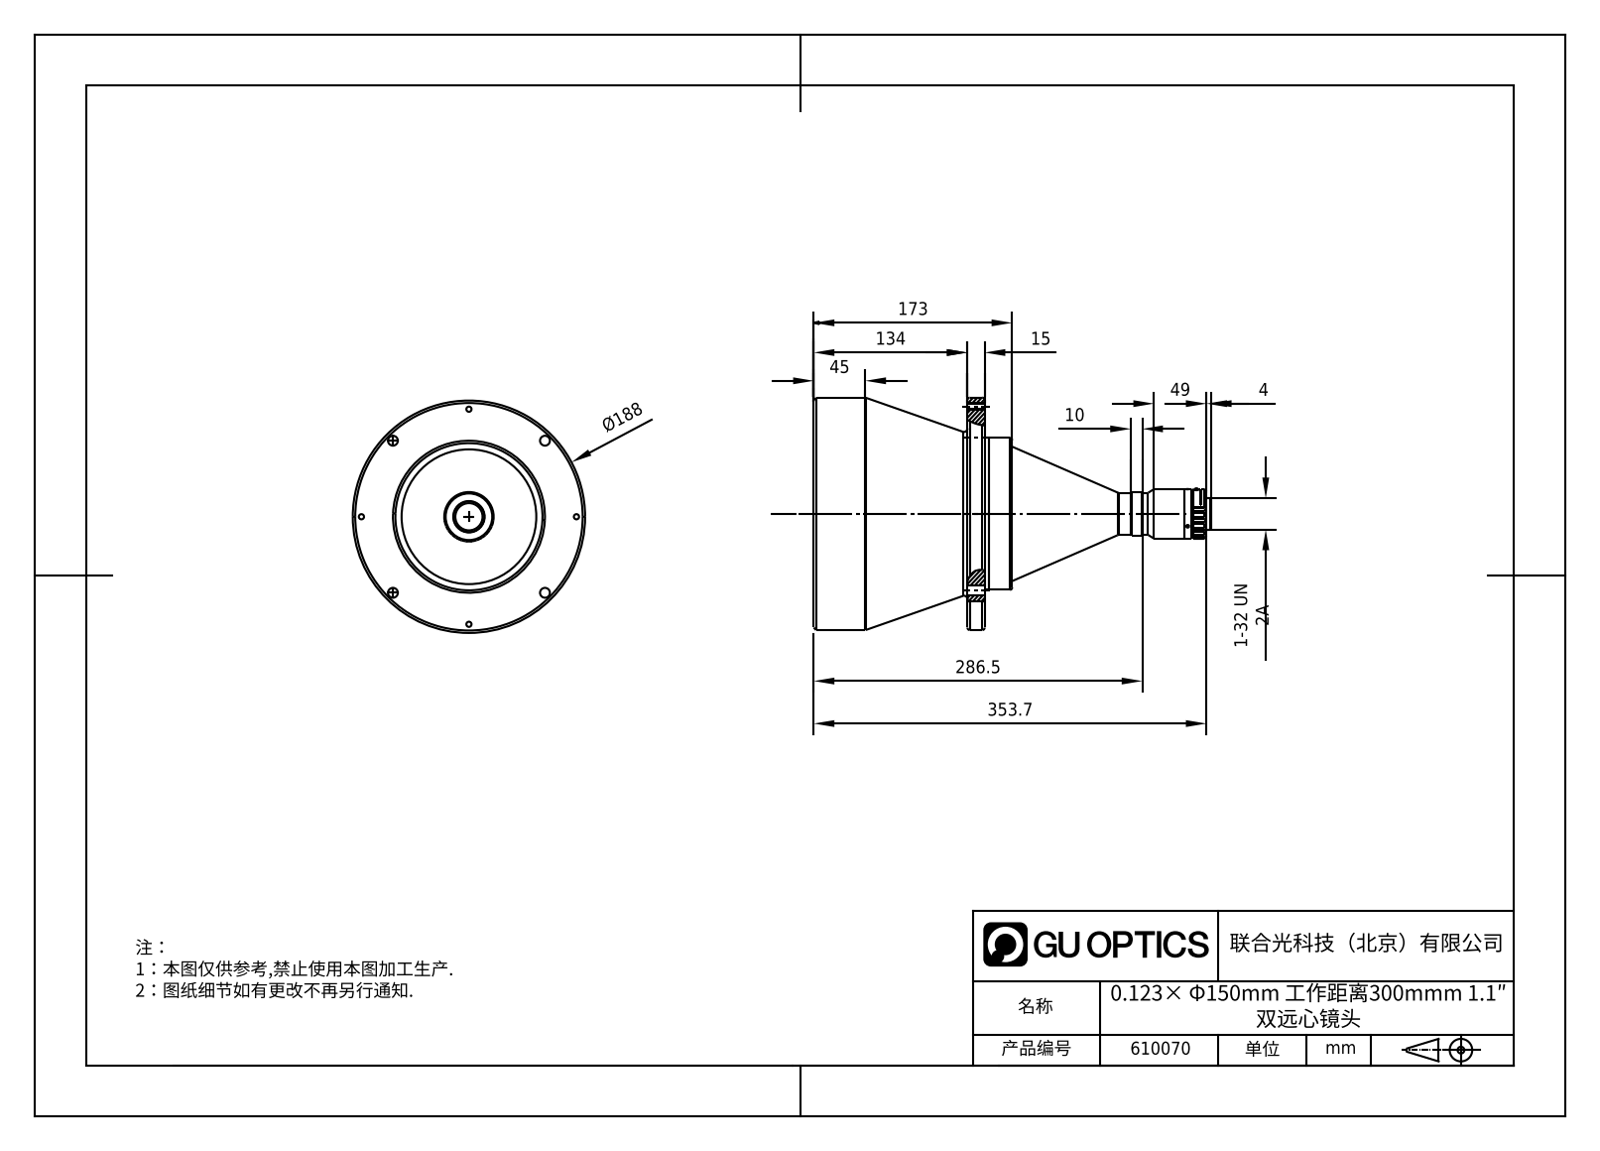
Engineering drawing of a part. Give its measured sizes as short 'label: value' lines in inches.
name: DTCM111-150-AL
written by: SolidWorks 2017 (CONFIG_CONTROL_DESIGN)
unit: in
bodies: 1 solid, 162 faces (21 planar, 89 cylindrical, 52 other)
size: 14.078 × 7.402 × 7.402
volume: 255.9 in³; area: 291.3 in²
holes: 4× ⌀0.165, 4× ⌀0.315, 3× ⌀0.098, 1× ⌀4.291, 1× ⌀6.909
bosses: 1× ⌀7.402, 1× ⌀4.843, 1× ⌀1.575, 1× ⌀1.437, 1× ⌀1.378, 1× ⌀1.339, 1× ⌀1.283, 1× ⌀1
rounds: 14× R0.118, 7× R0.157, 1× R0.04, 1× R0.055, 1× R0.094
face distances: 0.591, 5.276, 5.866, 6.811, 1.535, 0.945, 13.924, 8.649, 8.058, 7.113
hole spacings: 2.622, 3.425, 4.844, 6.329, 6.85
